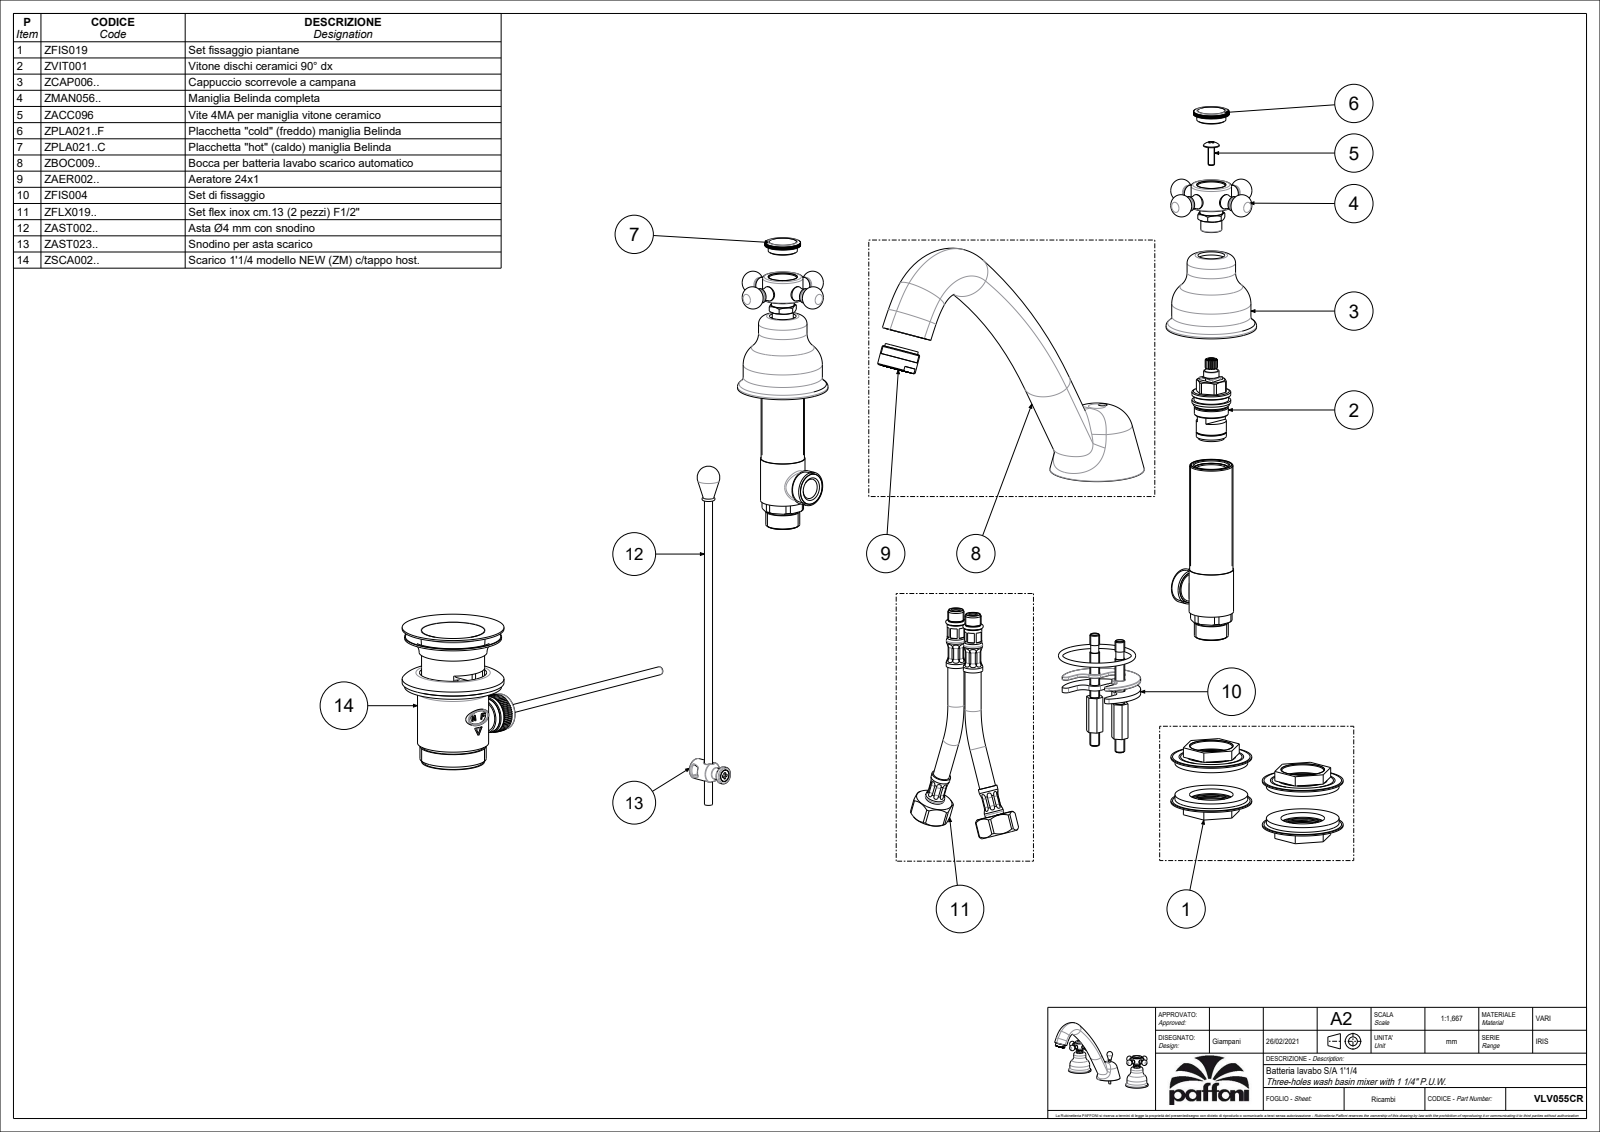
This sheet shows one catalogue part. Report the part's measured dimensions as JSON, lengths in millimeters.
{"part_name": "VLV055CR", "step_written_by": "CREO PARAMETRIC BY PTC INC, 2020044 (CONFIG_CONTROL_DESIGN)", "units": "millimeters", "bodies": {"solids": 9, "faces": 2917, "planar": 2003, "cylindrical": 521, "other": 393}, "overall_size": [264.07, 213.13, 165.42], "volume_mm3": 213874, "surface_area_mm2": 120893, "round_holes": [[5.5, 3], [17, 3], [4.5, 2], [8.8, 2], [9, 2], [10.3, 2], [11, 2], [16, 2], [16.2, 2], [16.3, 2], [19, 2], [25.7, 2]], "round_bosses_or_shafts": [[24, 3], [9, 3], [7, 3], [5, 3], [55, 2], [49, 2], [29.5, 2], [28, 2]], "partial_cylinders_radius": [[0.1, 34], [1, 12], [2.5, 8], [0.8, 5], [0.5, 4], [5, 2], [9.4, 2], [11, 2]], "face_to_face_distances": [3, 3.8, 0.8, 1.2, 0.5, 8.2, 7, 4, 5.2, 1.8], "hole_center_spacings": [9.6, 11.7, 13.31, 14.21, 15.4, 23.82, 89.45, 92.69]}
